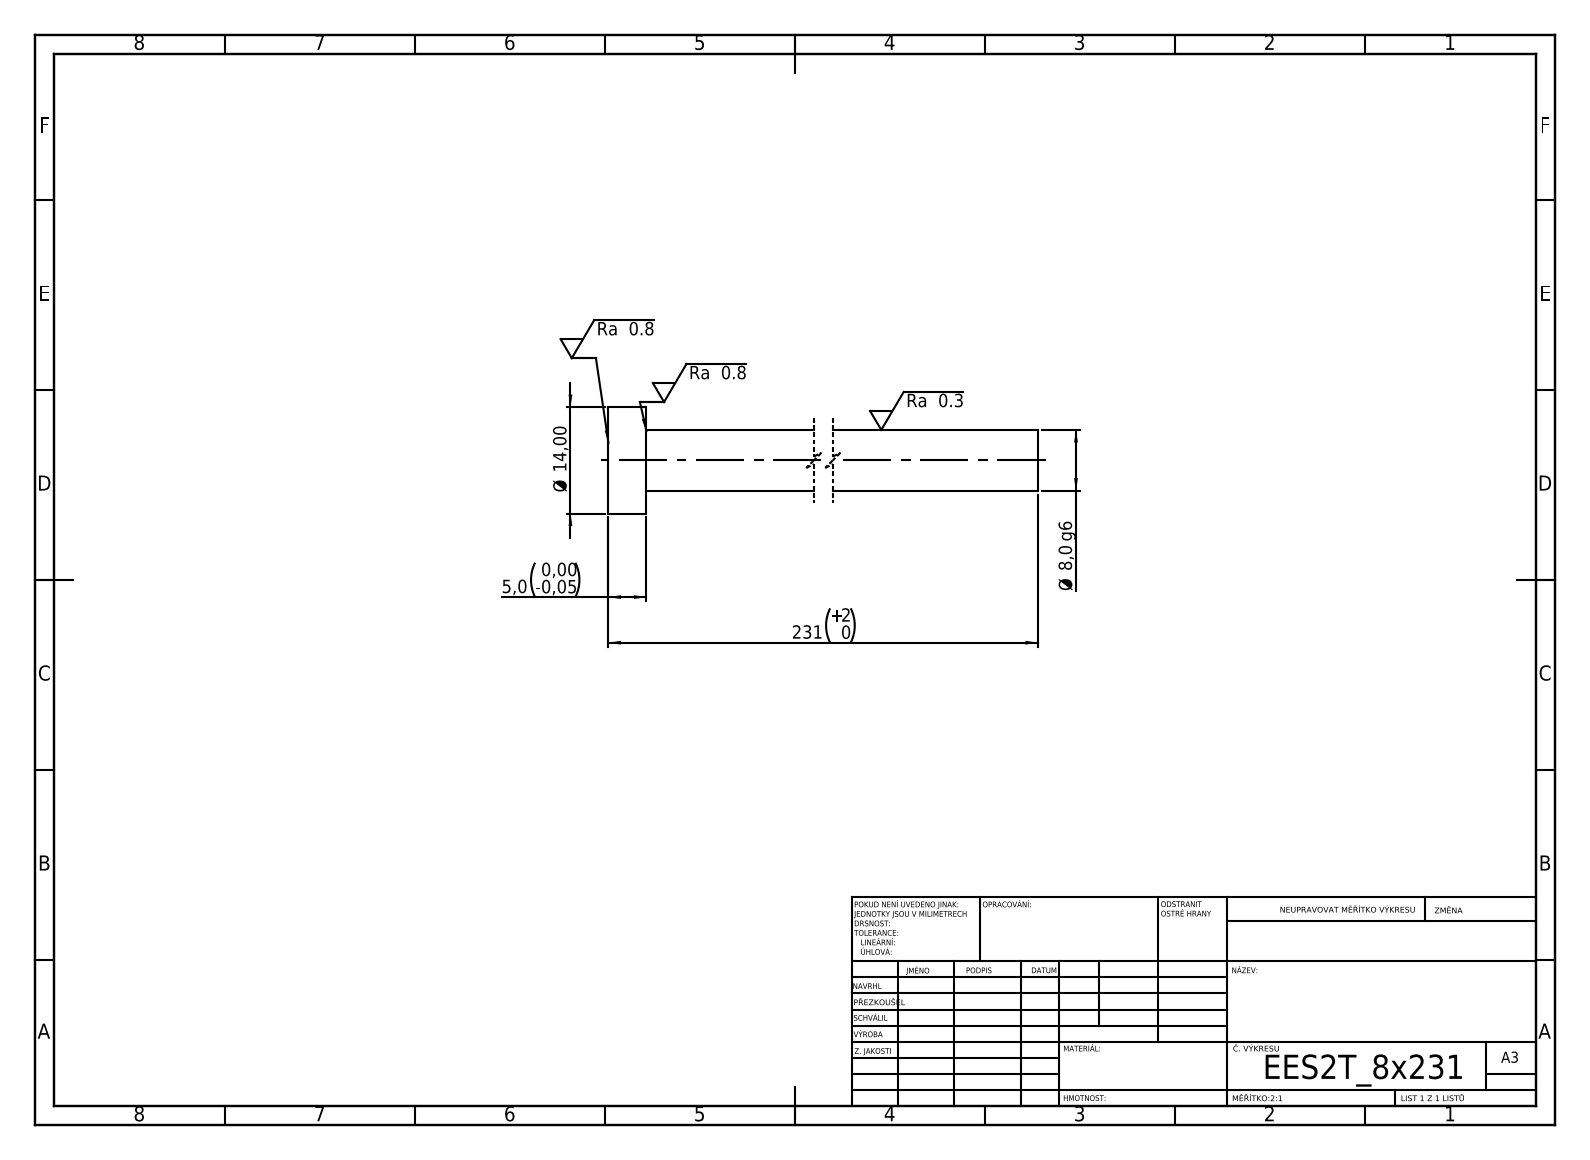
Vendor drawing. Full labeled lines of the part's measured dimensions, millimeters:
STEP written by: SolidWorks 2019 (CONFIG_CONTROL_DESIGN)
Units: millimetres
Bodies: 1 solid, 7 faces (3 planar, 4 cylindrical, 0 other)
Overall size (bounding box): 231 × 14 × 14
Volume: 12 130 mm³ · Surface area: 6 208 mm²
Round bosses / shafts (diameter × count): ⌀14 ×1, ⌀8 ×1
Main face-to-face distances: 5, 231, 226
